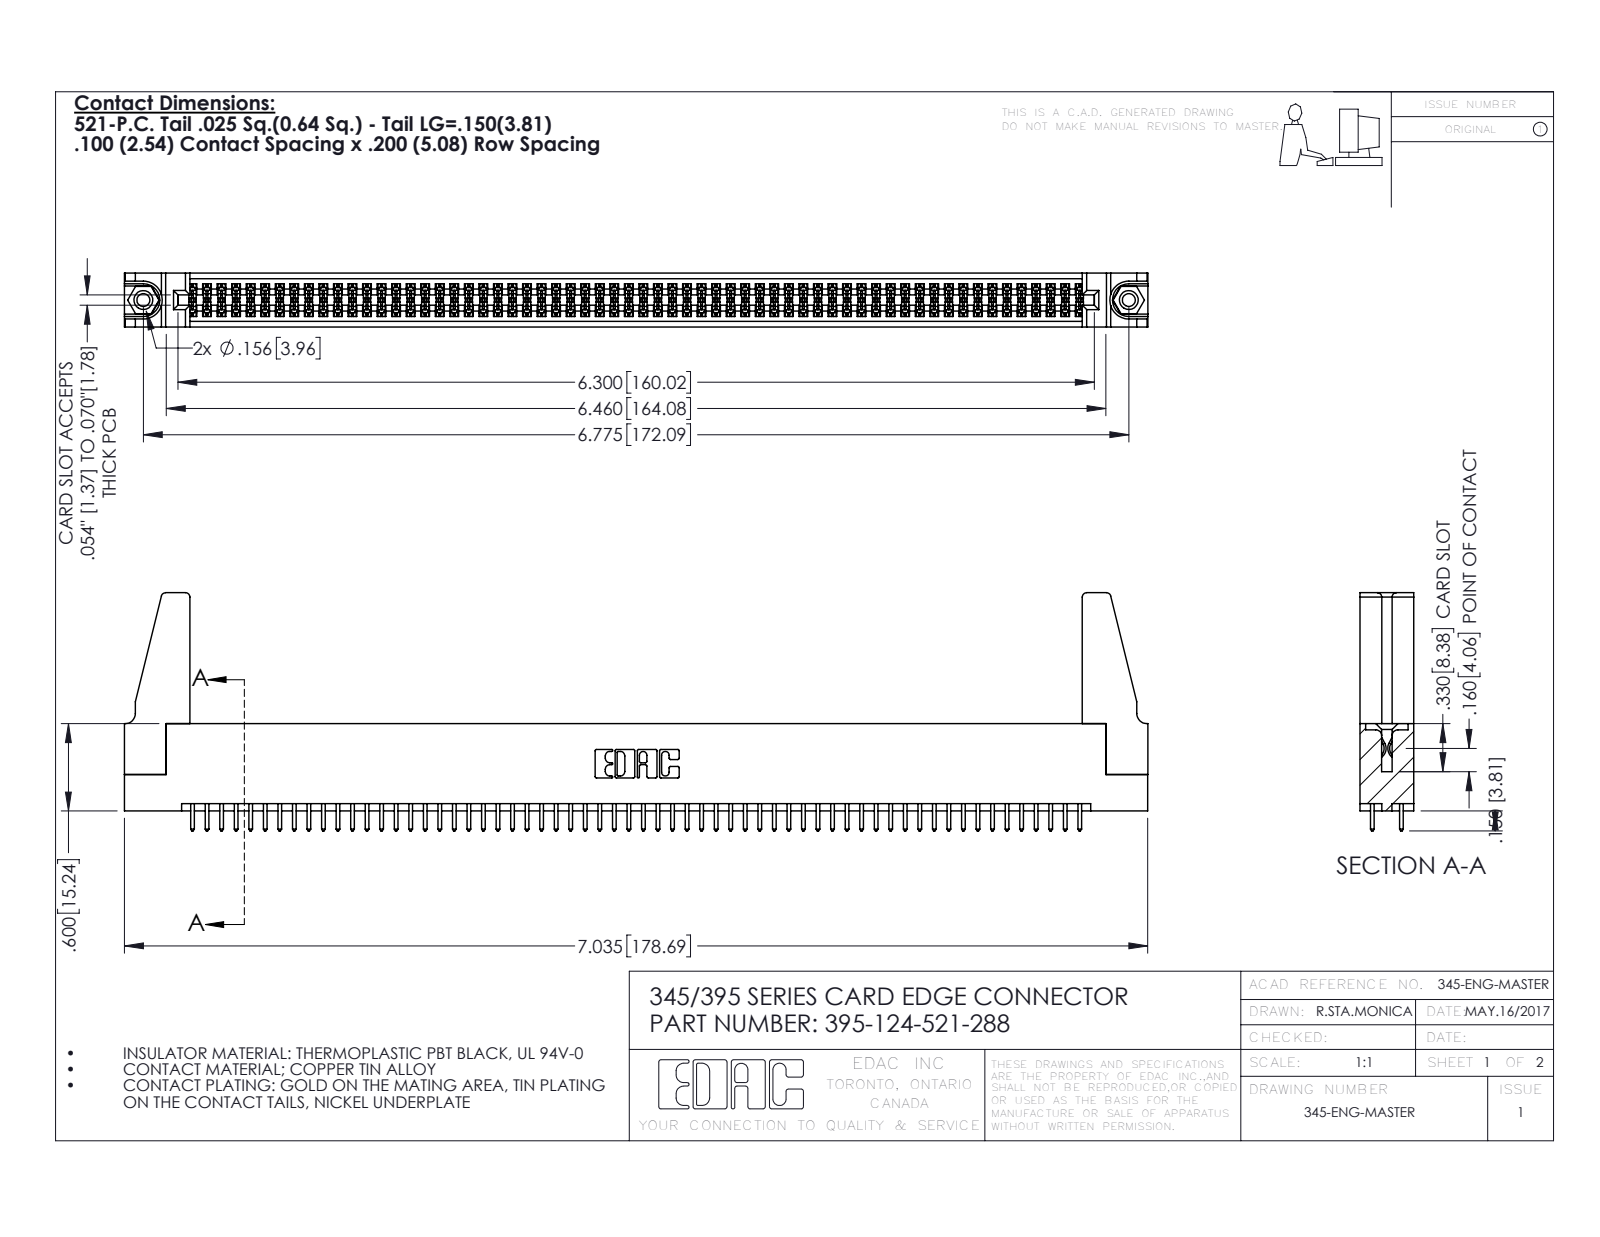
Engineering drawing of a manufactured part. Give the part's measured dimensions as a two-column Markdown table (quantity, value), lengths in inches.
| quantity | value |
| --- | --- |
| part name | 345-220-078_345-220-088; 345-292-001_345-293-121; 395-124-521-288; 345-250-001_345-250-001-102 (+1 more) |
| STEP written by | SolidWorks 2016 (CONFIG_CONTROL_DESIGN) |
| units | inches |
| bodies | 129 solids, 6450 faces (4244 planar, 2190 cylindrical, 16 other) |
| overall size | 7.036 × 1.637 × 0.37 |
| volume | 1.266 in³ |
| surface area | 45.01 in² |
| round holes (diameter × count) | 0.089 × 2, 0.125 × 2, 0.156 × 2, 0.064 × 1 |
| round bosses / shafts (diameter × count) | 0.155 × 2 |
| partial cylindrical surfaces (radius × count) | 0.006 × 186, 0.01 × 124, 0.01 × 22, 0.03 × 8, 0.007 × 6, 0.031 × 6, 0.026 × 3, 0.014 × 2 |
| main face-to-face distances | 0.072, 0.298, 0.37, 0.2, 0.098, 0.272, 0.025, 0.225, 0.175, 0.149 |
| hole center spacings | 0.27, 6.539, 6.775 |
